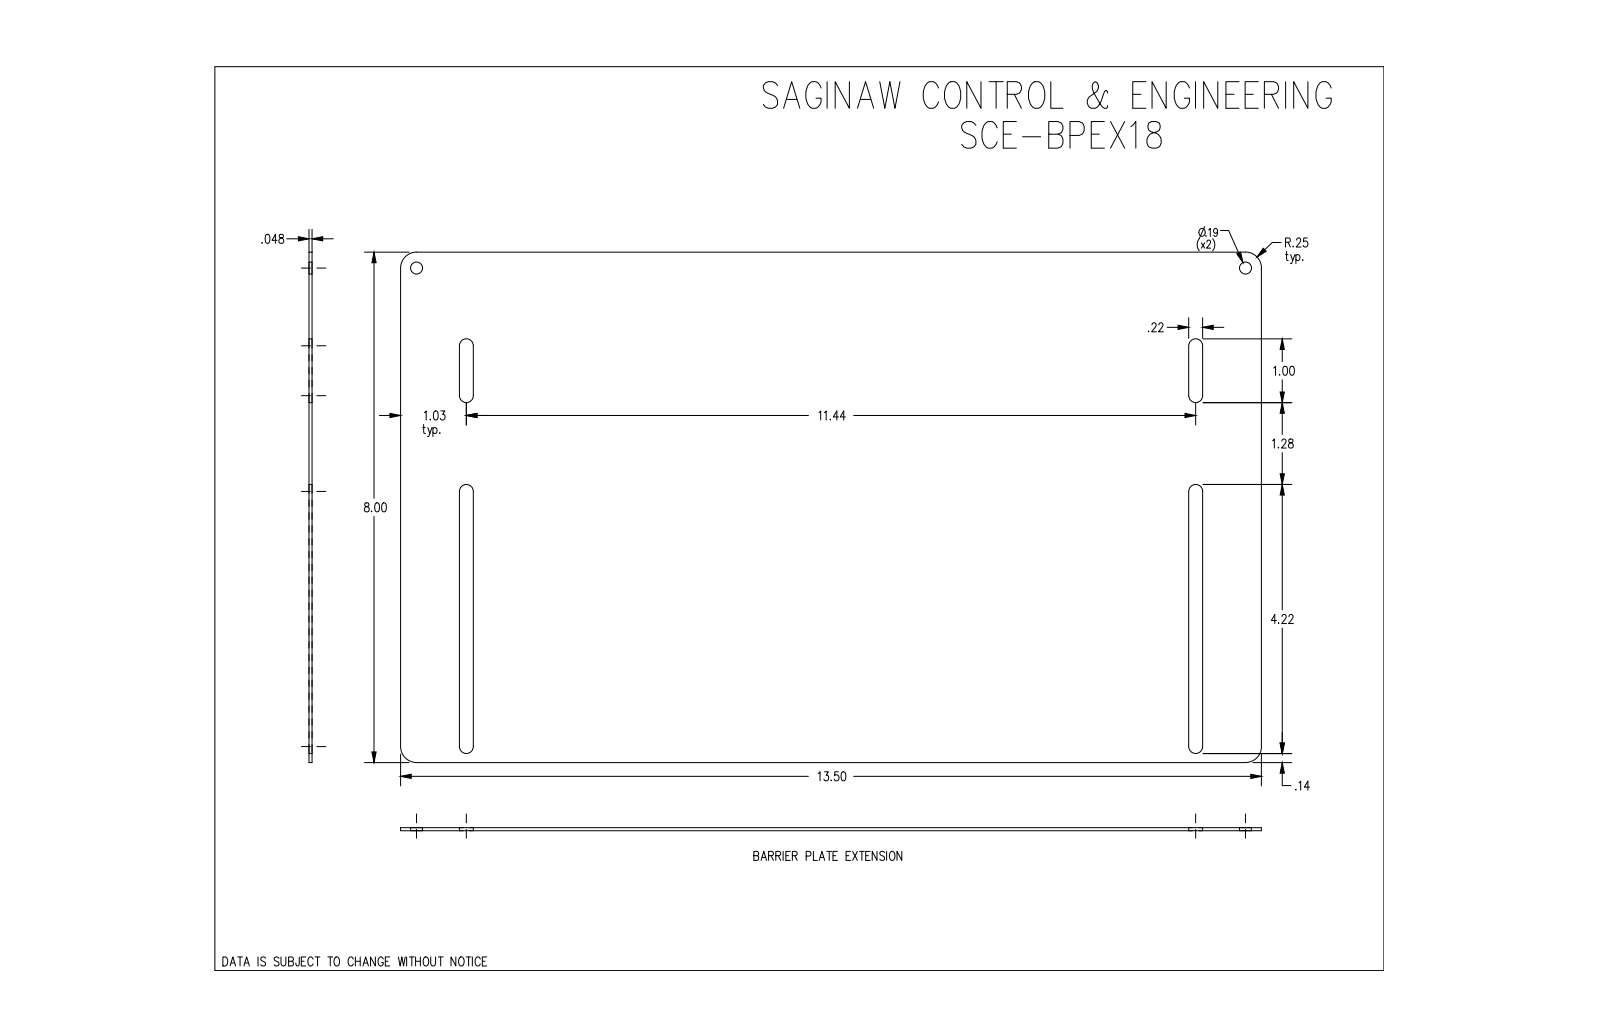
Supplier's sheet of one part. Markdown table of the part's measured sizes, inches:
| quantity | value |
| --- | --- |
| part name | SCE-BPEX18 |
| STEP written by | SolidWorks 2019 (CONFIG_CONTROL_DESIGN) |
| units | inches |
| bodies | 1 solid, 28 faces (14 planar, 14 cylindrical, 0 other) |
| overall size | 13.5 × 8 × 0.048 |
| volume | 5.072 in³ |
| surface area | 214.5 in² |
| round holes (diameter × count) | 0.187 × 2 |
| partial cylindrical surfaces (radius × count) | 0.109 × 8, 0.25 × 4 |
| main face-to-face distances | 0.048, 8, 0.922, 1.14, 12.36, 12.578, 0.218, 11.437, 13.5, 11.655 |
| hole center spacings | 13 |
